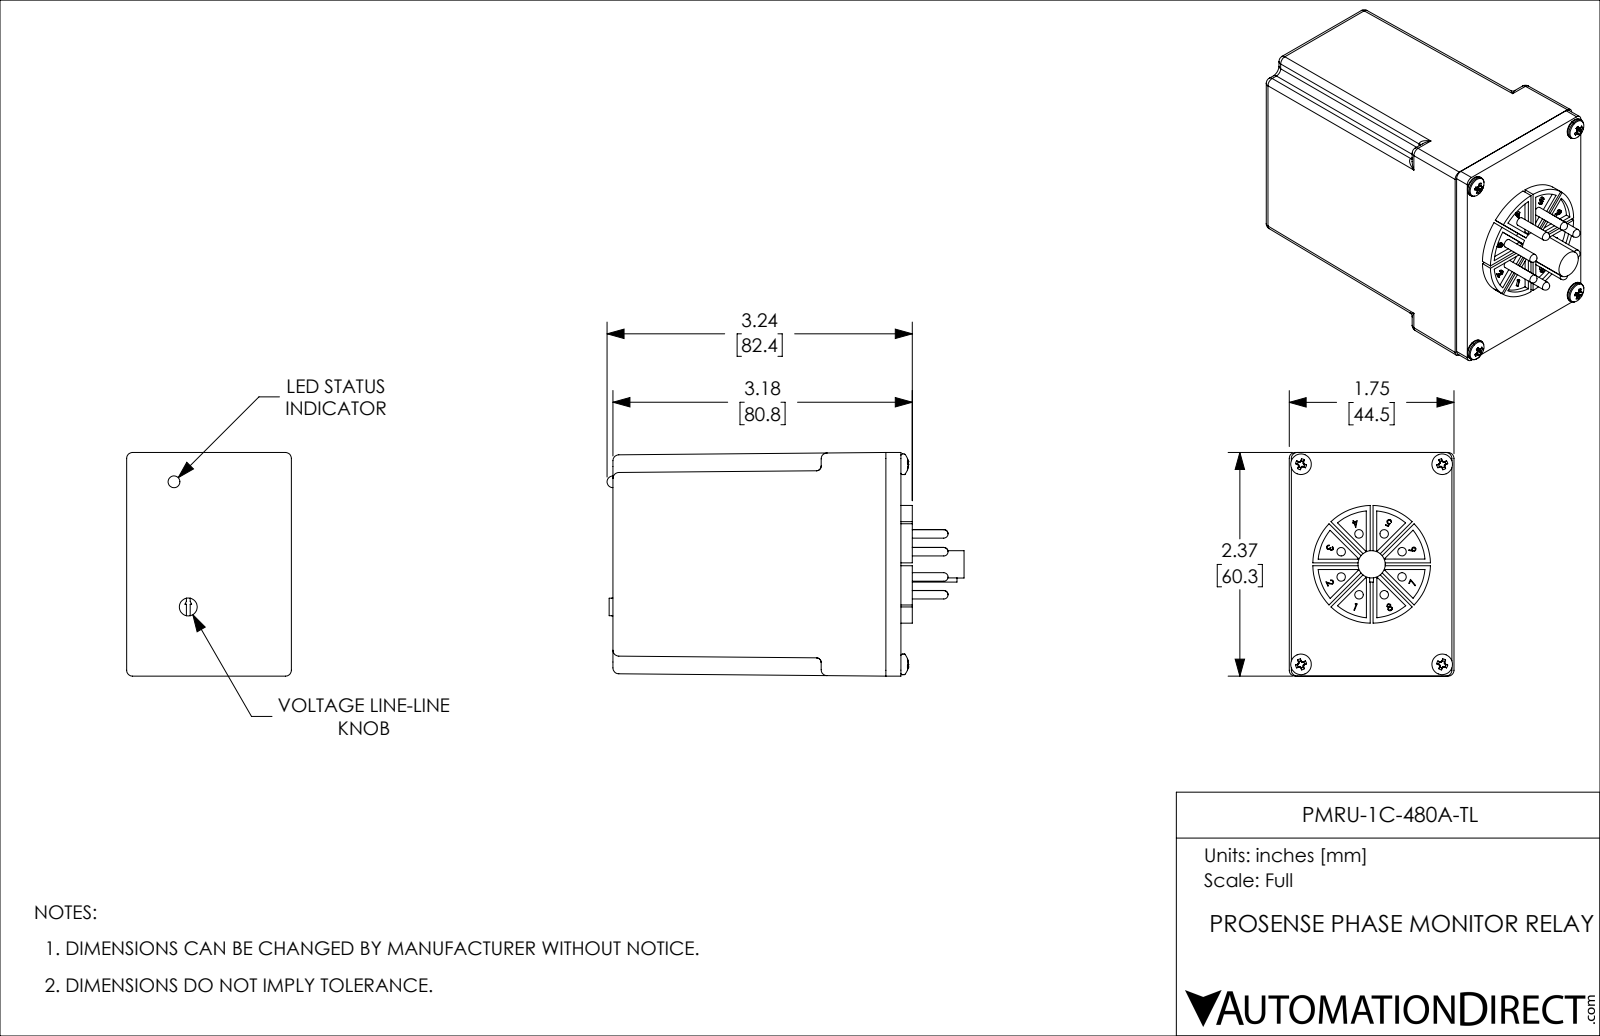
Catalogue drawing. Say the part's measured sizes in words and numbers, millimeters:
The part is named "PMRU-1C-480A-TL". Its 3-D file was written by "SolidWorks 2019 (CONFIG_CONTROL_DESIGN)". It is 16 solids with 695 faces: 229 planar, 282 cylindrical and 184 other. Overall it measures 96.3 by 60.3 by 44.5 millimeters. Its volume is 200 600 cubic millimeters and its surface area 28 830 square millimeters. Round holes: 4 of diameter 3.2. Round bosses or shafts: 8 of diameter 2.3, 4 of diameter 5.6, 4 of diameter 2.8, 4 of diameter 2, 1 of diameter 31.8, 1 of diameter 7.4, 1 of diameter 4.8. Partial cylindrical surfaces (rounded edges, fillets, slot ends): 32 of radius 1.6, 8 of radius 0.1, 4 of radius 1.3, 1 of radius 14.5. The main face-to-face distances are 73.7, 4.1, 77.7, 1.8, 5.8, 79.5, 4.8, 1.3, 3, 7.1. The hole center spacings are 38.1, 54, 66.1.
